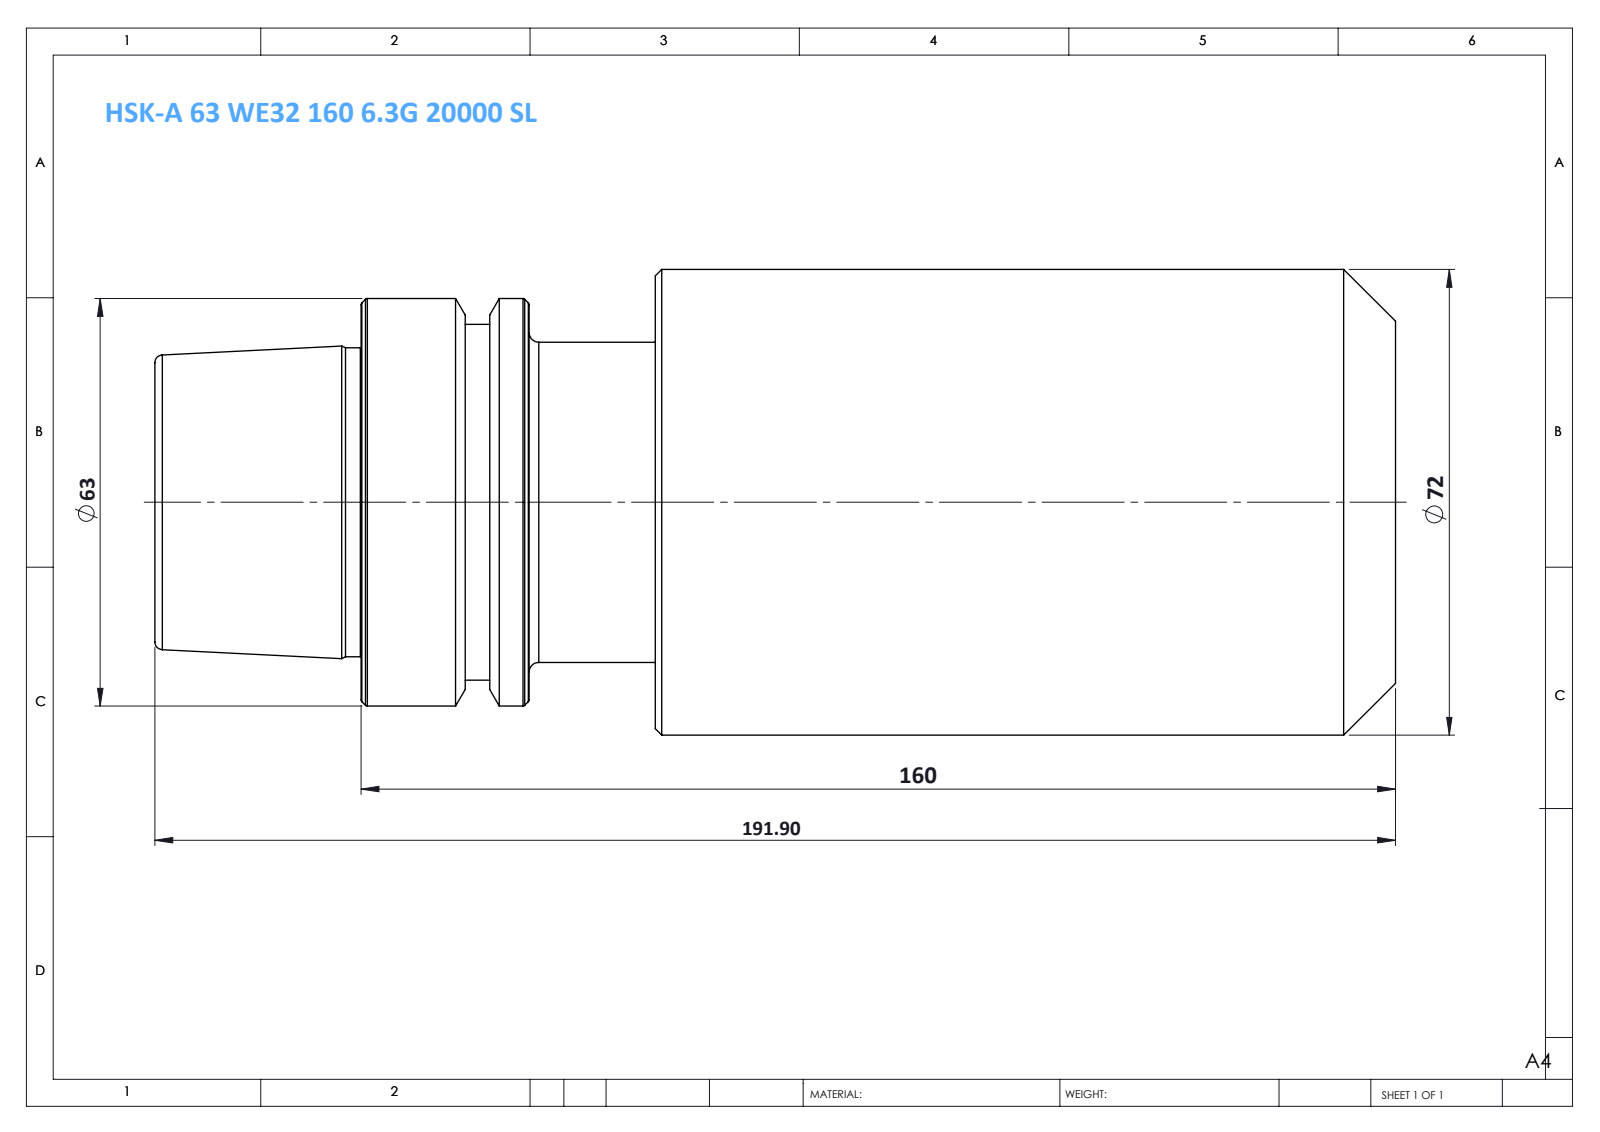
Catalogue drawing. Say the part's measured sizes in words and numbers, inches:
The part is named "HSK-A 63 WE32 160 6.3G 20000 SL". Its 3-D file was written by "SolidWorks 2014 (CONFIG_CONTROL_DESIGN)". It is 1 solid with 51 faces: 7 planar, 12 cylindrical and 32 other. Overall it measures 7.555 by 2.835 by 2.835 inches. Its volume is 38.42 cubic inches and its surface area 75.17 square inches. Round bosses or shafts: 1 of diameter 2.835, 1 of diameter 2.48, 1 of diameter 2.165, 1 of diameter 1.949, 1 of diameter 1.881. The main face-to-face distances are 4.508, 7.555, 3.047, 5.276, 0.768, 2.28, 6.299, 1.791, 1.024, 1.256.
